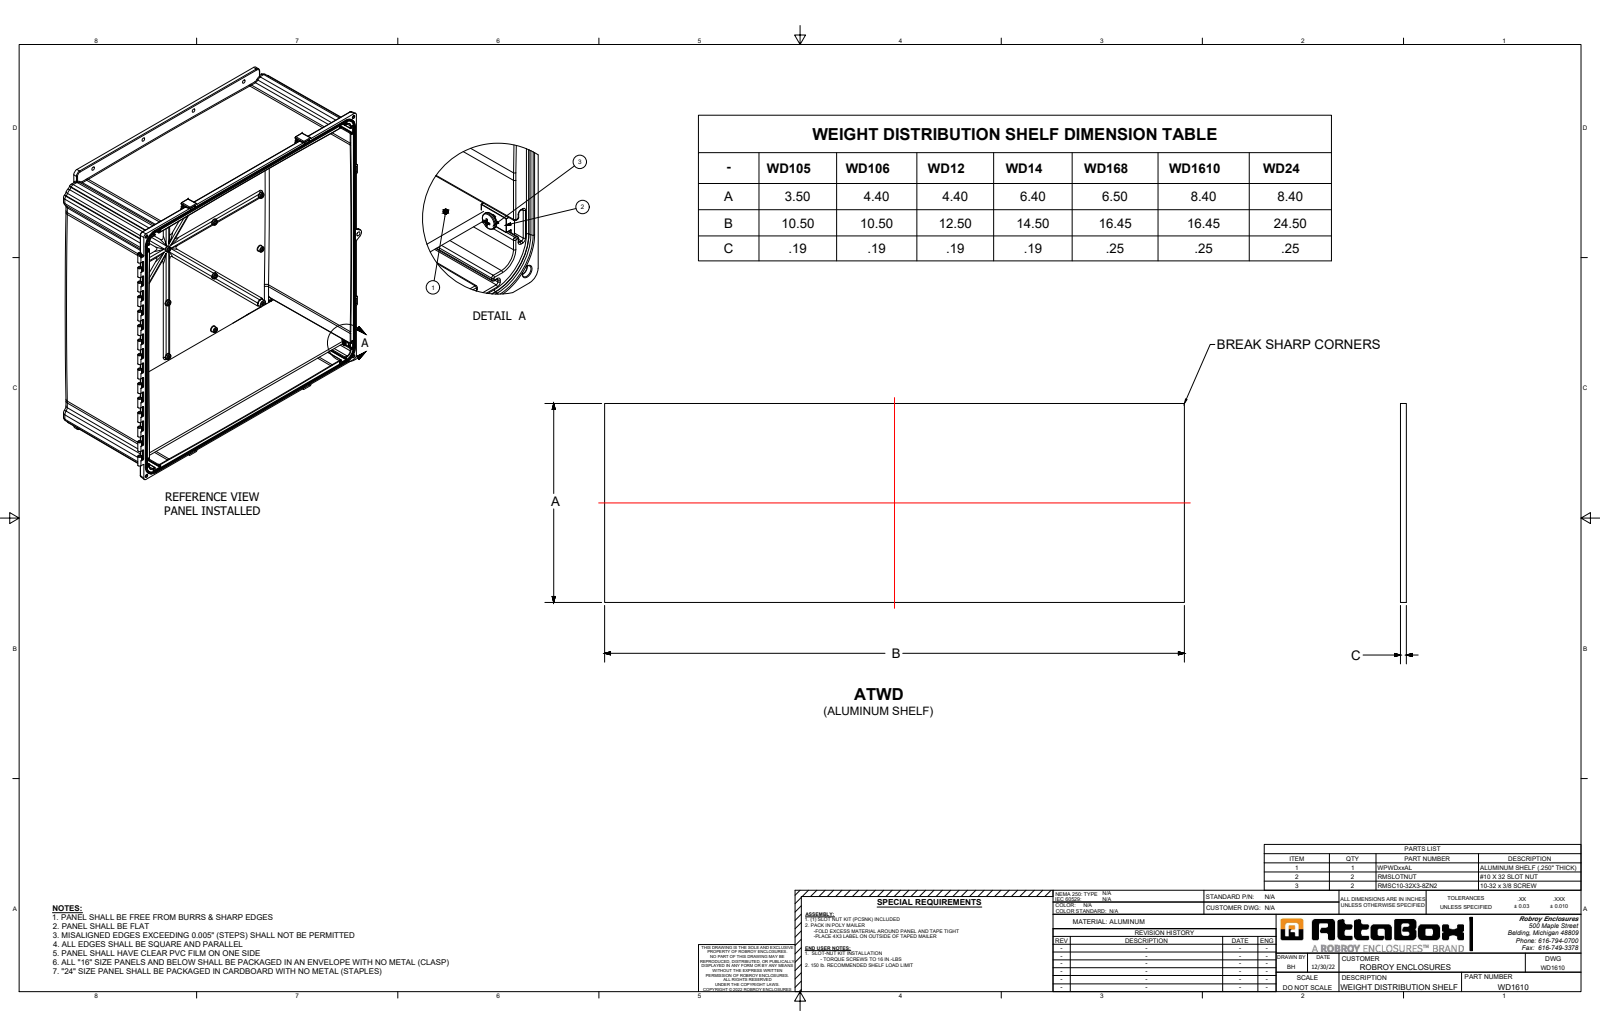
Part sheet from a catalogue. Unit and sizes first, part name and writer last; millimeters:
Units: millimetres
Overall size (bounding box): 417.8 × 165.1 × 4.8
Main face-to-face distances: 4.8, 165.1, 417.8
Volume: 333 000 mm³ · Surface area: 143 600 mm²
Bodies: 1 solid, 6 faces (6 planar, 0 cylindrical, 0 other)
Part name (STEP PRODUCT): WD16-10_Default
STEP written by: SolidWorks 2023 (CONFIG_CONTROL_DESIGN)
